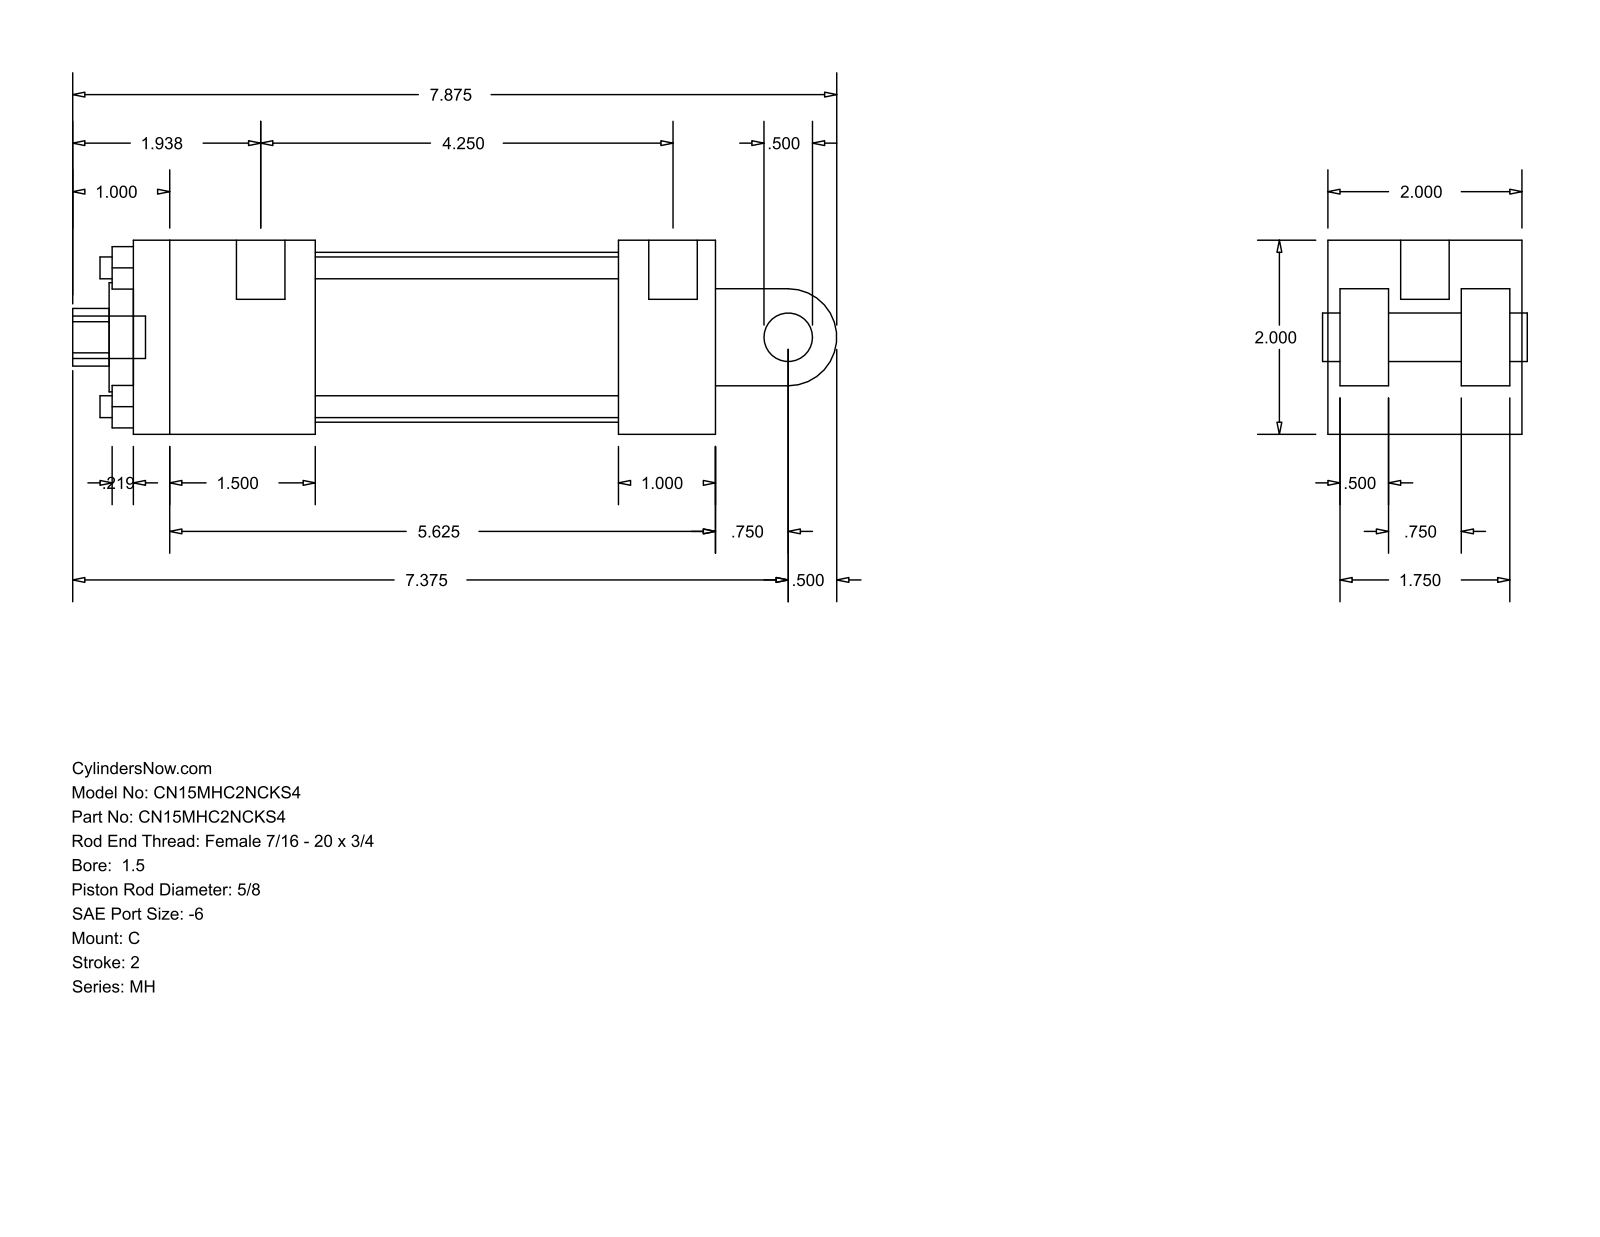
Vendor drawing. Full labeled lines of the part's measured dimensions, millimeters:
Part name (STEP PRODUCT): MH_C__0150_0.625
STEP written by: GSSL Pune (CONFIG_CONTROL_DESIGN)
Units: millimetres
Bodies: 0 solids, 99 faces (70 planar, 29 cylindrical, 0 other)
Overall size (bounding box): 200.03 × 50.8 × 50.8
Round holes (diameter × count): ⌀5.71 ×4, ⌀5.56 ×2, ⌀12.7 ×1, ⌀15.88 ×1, ⌀28.57 ×1, ⌀44.45 ×1
Round bosses / shafts (diameter × count): ⌀12.7 ×2, ⌀5.56 ×2, ⌀11.11 ×1
Partial cylindrical surfaces — rounded edges, fillets, slot ends (radius × count): R7.54 ×1, R12.7 ×1
Main face-to-face distances: 50.8, 12.7, 152.4, 25.4, 3.17, 47.63, 15.87, 34.93, 31.76, 38.1
Hole centre spacings: 25.68, 36.32, 51.36
